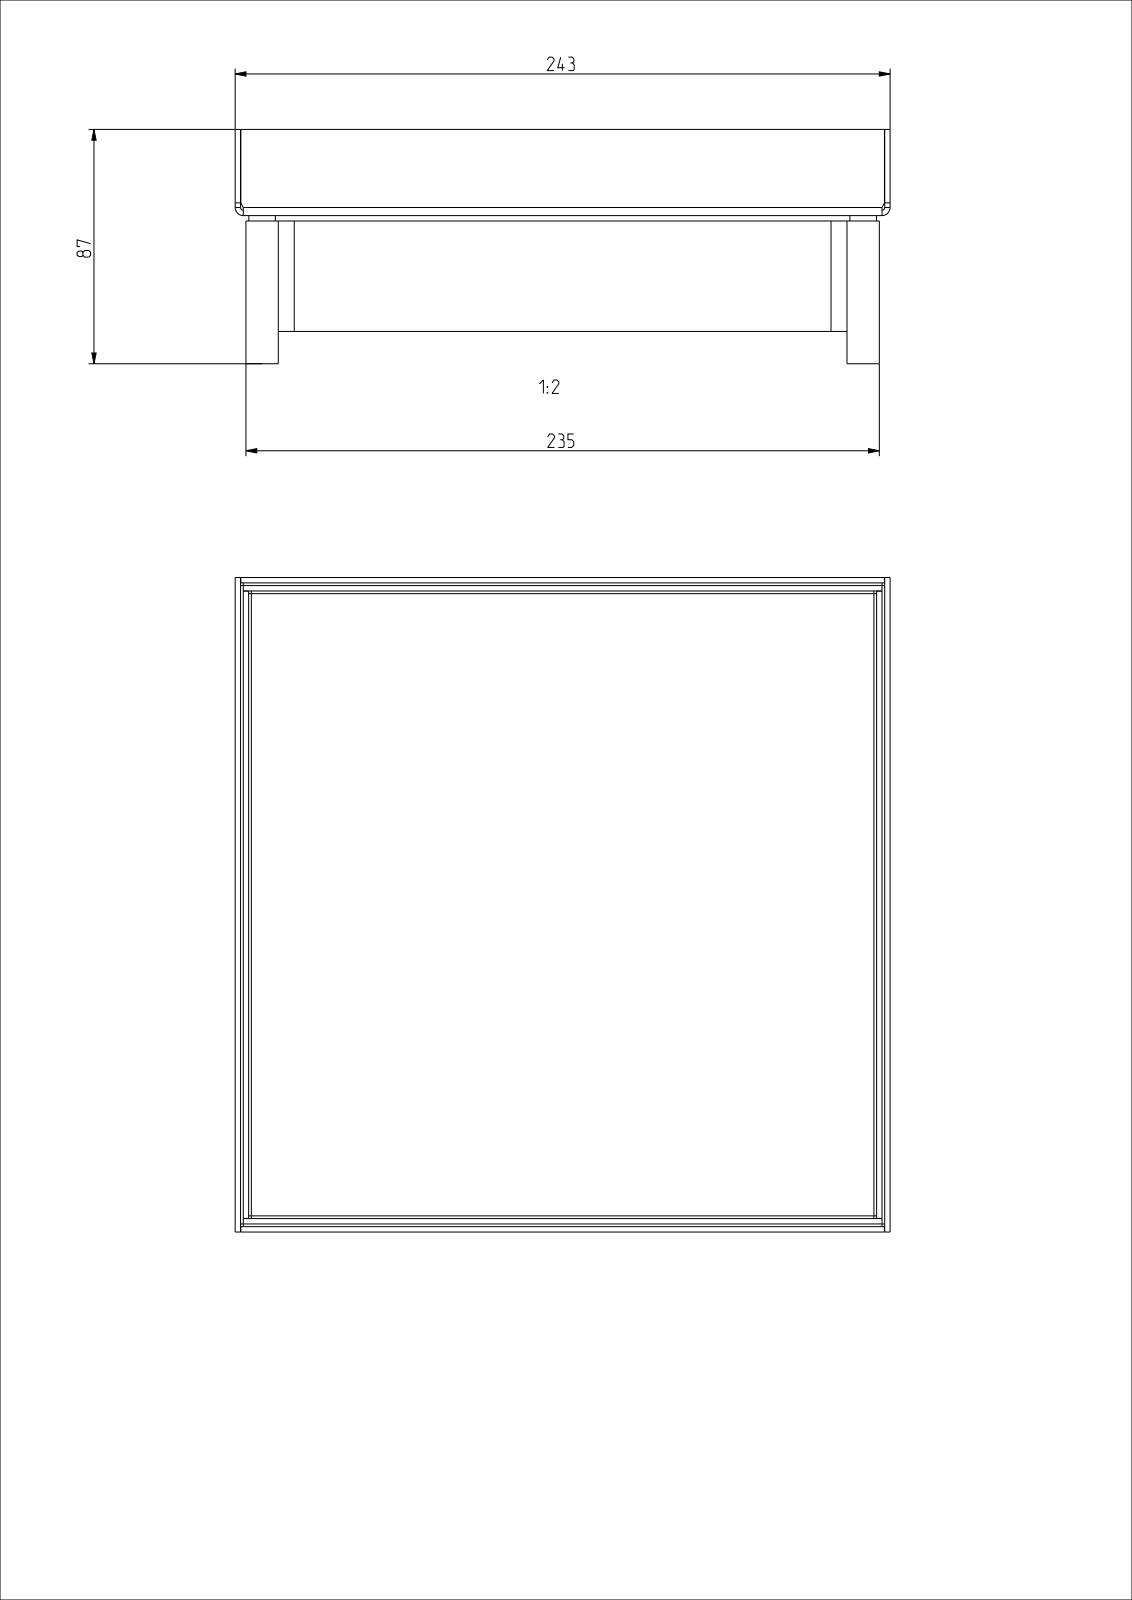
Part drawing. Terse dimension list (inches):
name: T-00731; T-00632; T-00625; T-00829_ASM (+3 more)
written by: CREO PARAMETRIC BY PTC INC, 2022024 (AUTOMOTIVE_DESIGN)
unit: in
bodies: 7 solids, 166 faces (110 planar, 56 cylindrical, 0 other)
size: 9.567 × 9.567 × 3.425
volume: 20.36 in³; area: 509.6 in²
holes: 4× ⌀0.268, 4× ⌀0.335
bosses: 4× ⌀0.472, 4× ⌀0.388
rounds: 8× R0.039, 8× R0.118, 1× R5.906, 1× R6.004
face distances: 0.079, 0.118, 9.252, 9.37, 0.197, 0.098, 0.039, 9.134, 0.236, 9.488
hole spacings: 8.78, 12.416
